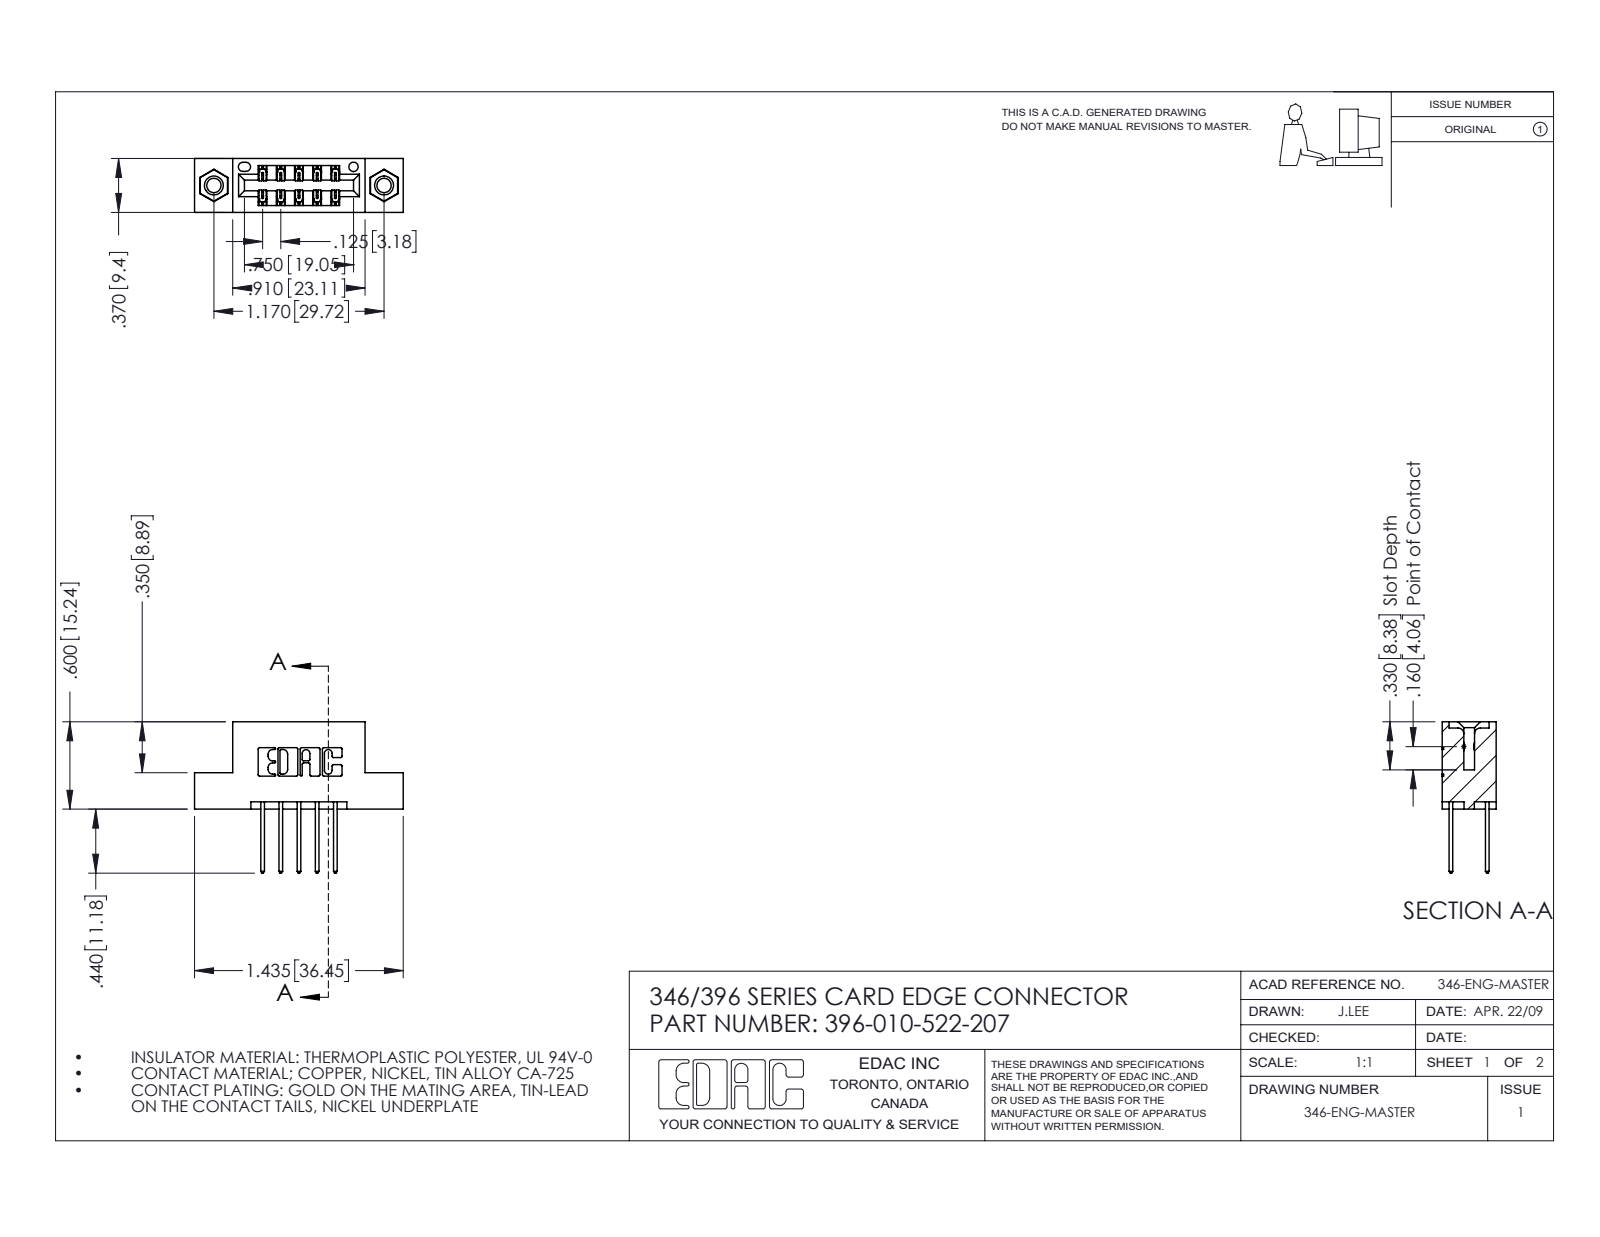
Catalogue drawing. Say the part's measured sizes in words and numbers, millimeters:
The part is named "396-010-522-207; 346 Part_Flush Mounting Lugs - 0.156 Dia-TI; 345-250-001_345-250-005-103; 345-292-001_345-293-122". Its 3-D file was written by "SolidWorks 2016 (CONFIG_CONTROL_DESIGN)". It is 13 solids with 702 faces: 458 planar, 228 cylindrical and 16 other. Overall it measures 36.4 by 26.4 by 9.4 millimeters. Its volume is 3 280 cubic millimeters and its surface area 4 078 square millimeters. Round holes: 2 of diameter 2.5, 2 of diameter 3.2, 2 of diameter 4, 1 of diameter 1.6. Round bosses or shafts: 2 of diameter 3.9. Partial cylindrical surfaces (rounded edges, fillets, slot ends): 22 of radius 0.3, 15 of radius 0.2, 10 of radius 0.3, 6 of radius 0.2, 6 of radius 0.8, 3 of radius 0.7, 2 of radius 0.4, 2 of radius 0.6. The main face-to-face distances are 6.4, 1.2, 8.2, 9.4, 0.6, 1.8, 7.6, 7, 3.8, 5.6. The hole center spacings are 6.2, 24.6, 29.7.
